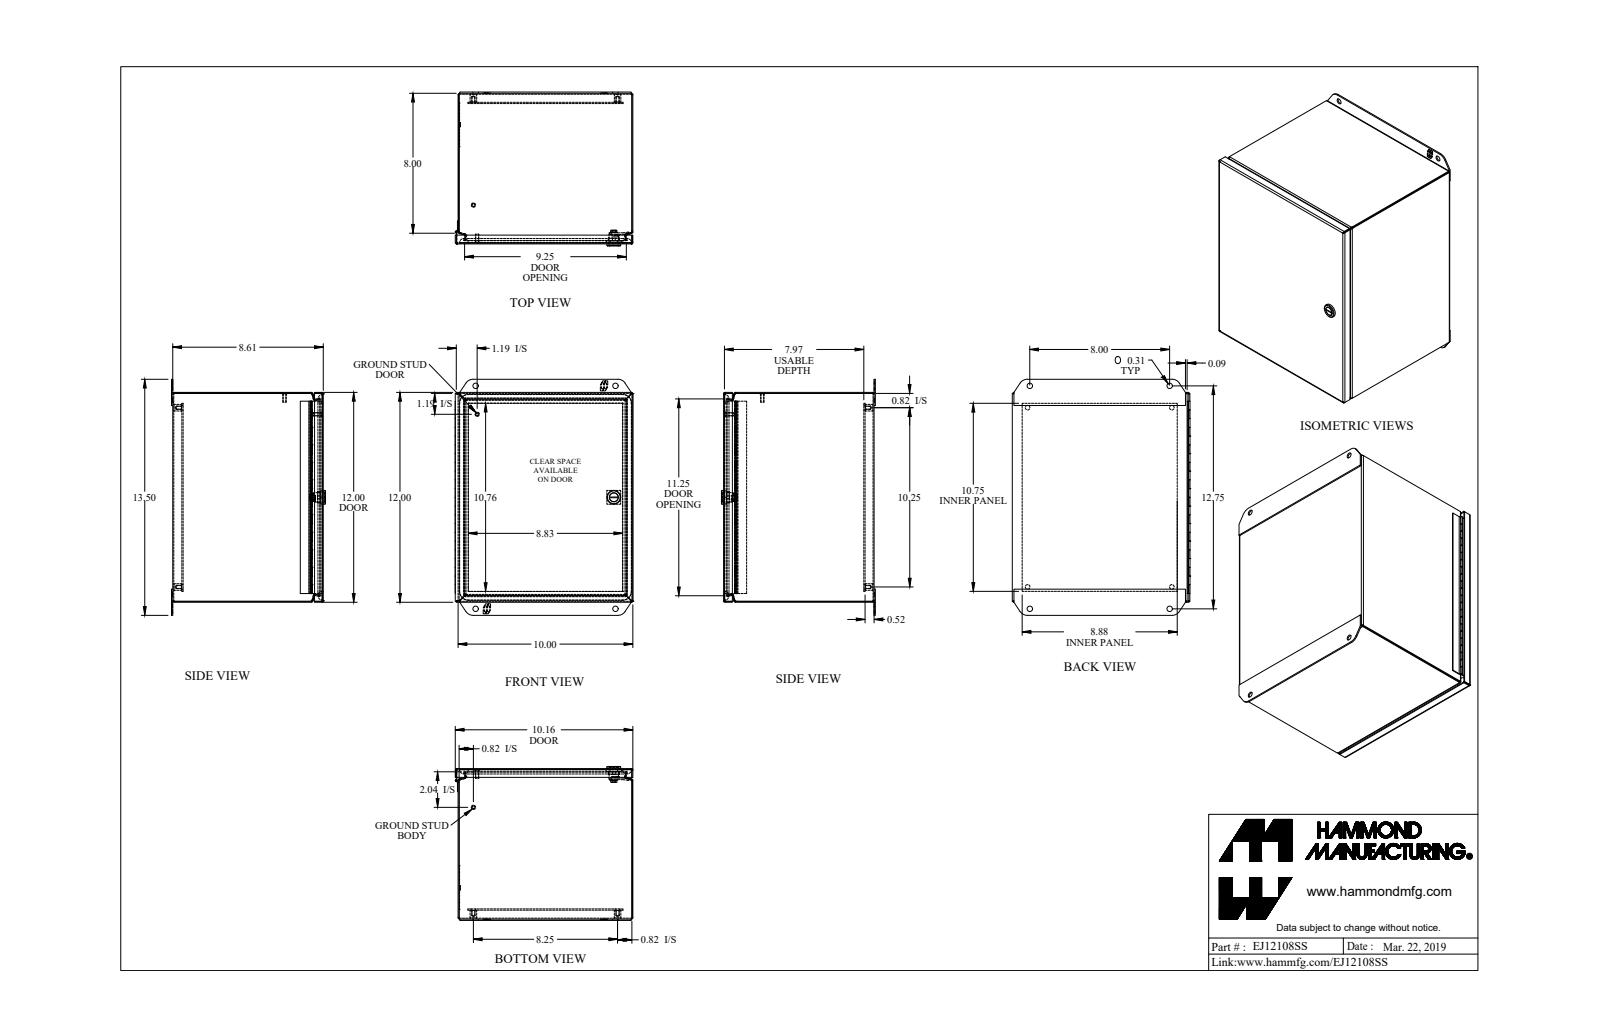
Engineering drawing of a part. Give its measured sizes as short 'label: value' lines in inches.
name: EJ12108SS_Default
written by: SolidWorks 2019 (CONFIG_CONTROL_DESIGN)
unit: in
bodies: 16 solids, 720 faces (402 planar, 222 cylindrical, 96 other)
size: 13.5 × 10.165 × 8.805
volume: 50.03 in³; area: 1 667 in²
holes: 4× ⌀0.156, 4× ⌀0.265, 4× ⌀0.313, 1× ⌀0.05, 1× ⌀0.516
bosses: 4× ⌀0.375, 2× ⌀0.25, 2× ⌀0.19, 1× ⌀0.788, 1× ⌀0.535, 1× ⌀0.496, 1× ⌀0.435, 1× ⌀0.1
rounds: 16× R0.029, 16× R0.086, 12× R0.281, 4× R0.25, 4× R0.499, 4× R0.5, 2× R0.06, 1× R0.03
face distances: 0.057, 8.554, 9.943, 11.943, 0.072, 0.589, 8.611, 8.497, 8.094, 8.037
hole spacings: 1.256, 11.501, 10.25, 8.22, 13.158, 14.081, 5.13, 6.376
